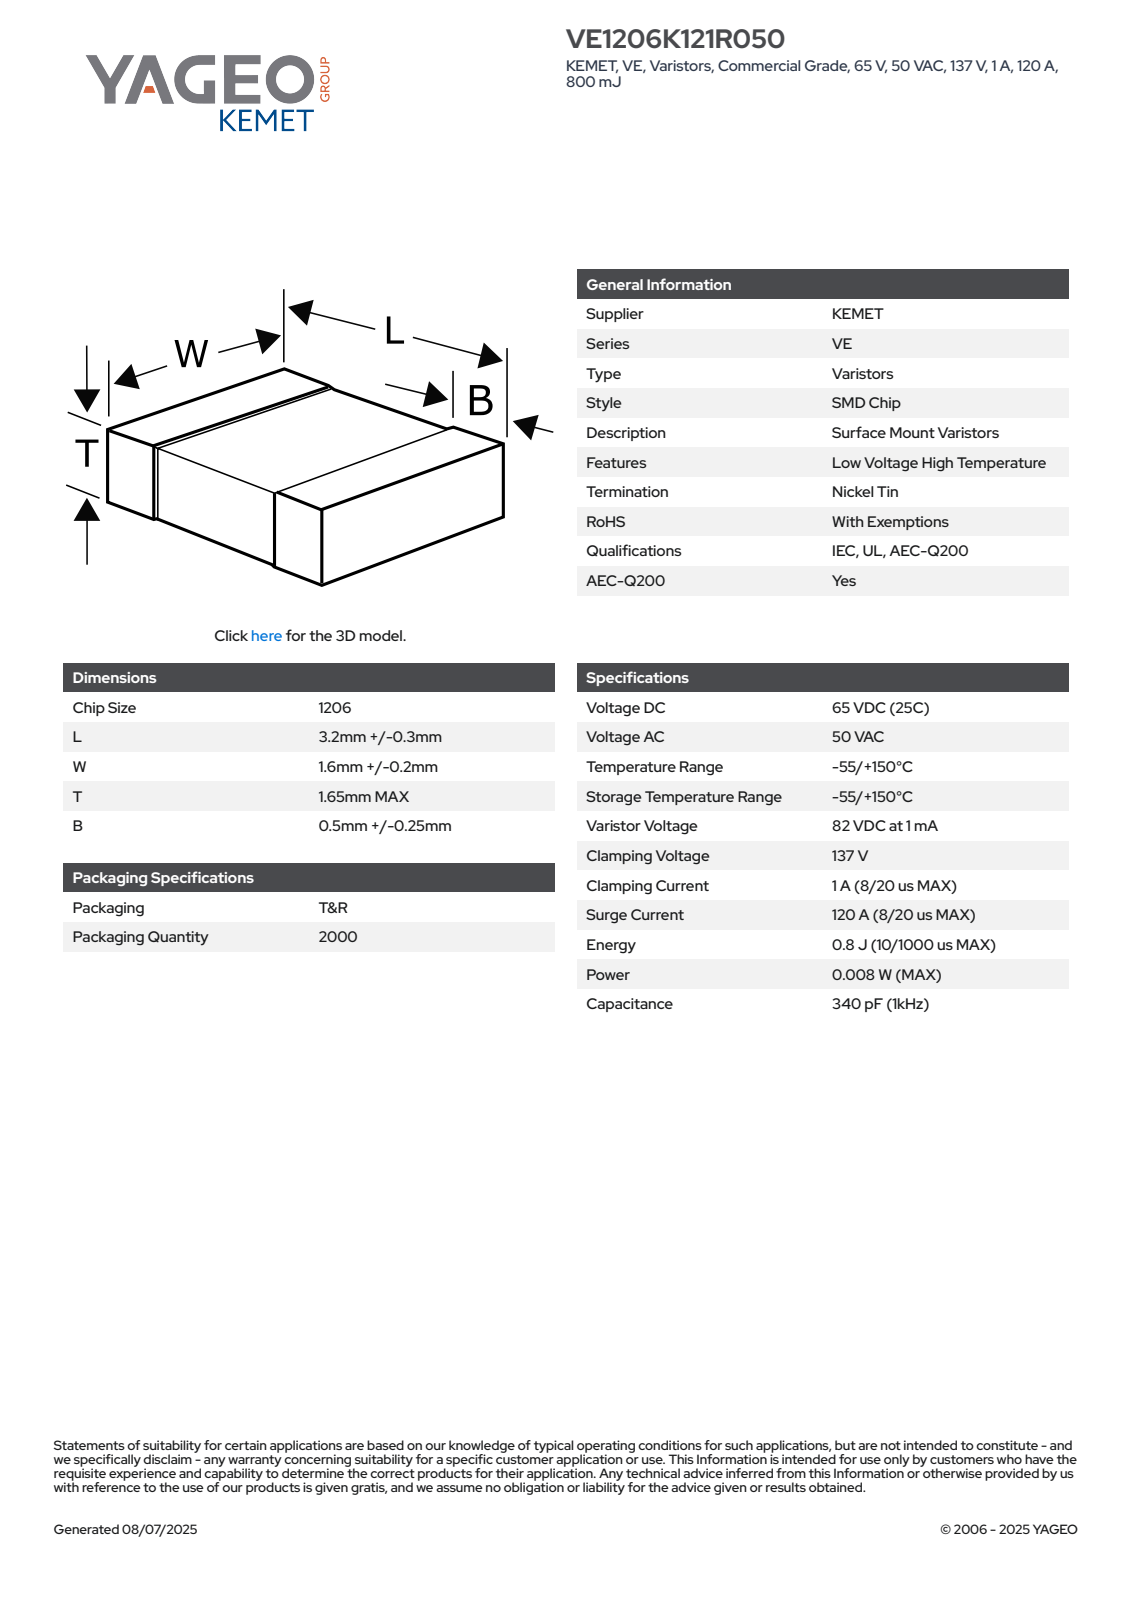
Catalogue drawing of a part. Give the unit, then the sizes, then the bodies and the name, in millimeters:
Units: millimetres
Overall size (bounding box): 3.5 × 1.8 × 1.65
Main face-to-face distances: 1.61, 1.76, 1.57, 1.72, 3.5, 1.65, 1.8, 1.62, 1.58, 1.63
Volume: 10 mm³ · Surface area: 30 mm²
Bodies: 4 solids, 125 faces (71 planar, 38 cylindrical, 16 other)
Part name (STEP PRODUCT): VS_SMD_1206_L3.5W1.8T1.65B0.75
STEP written by: SolidWorks 2021 (AUTOMOTIVE_DESIGN)
